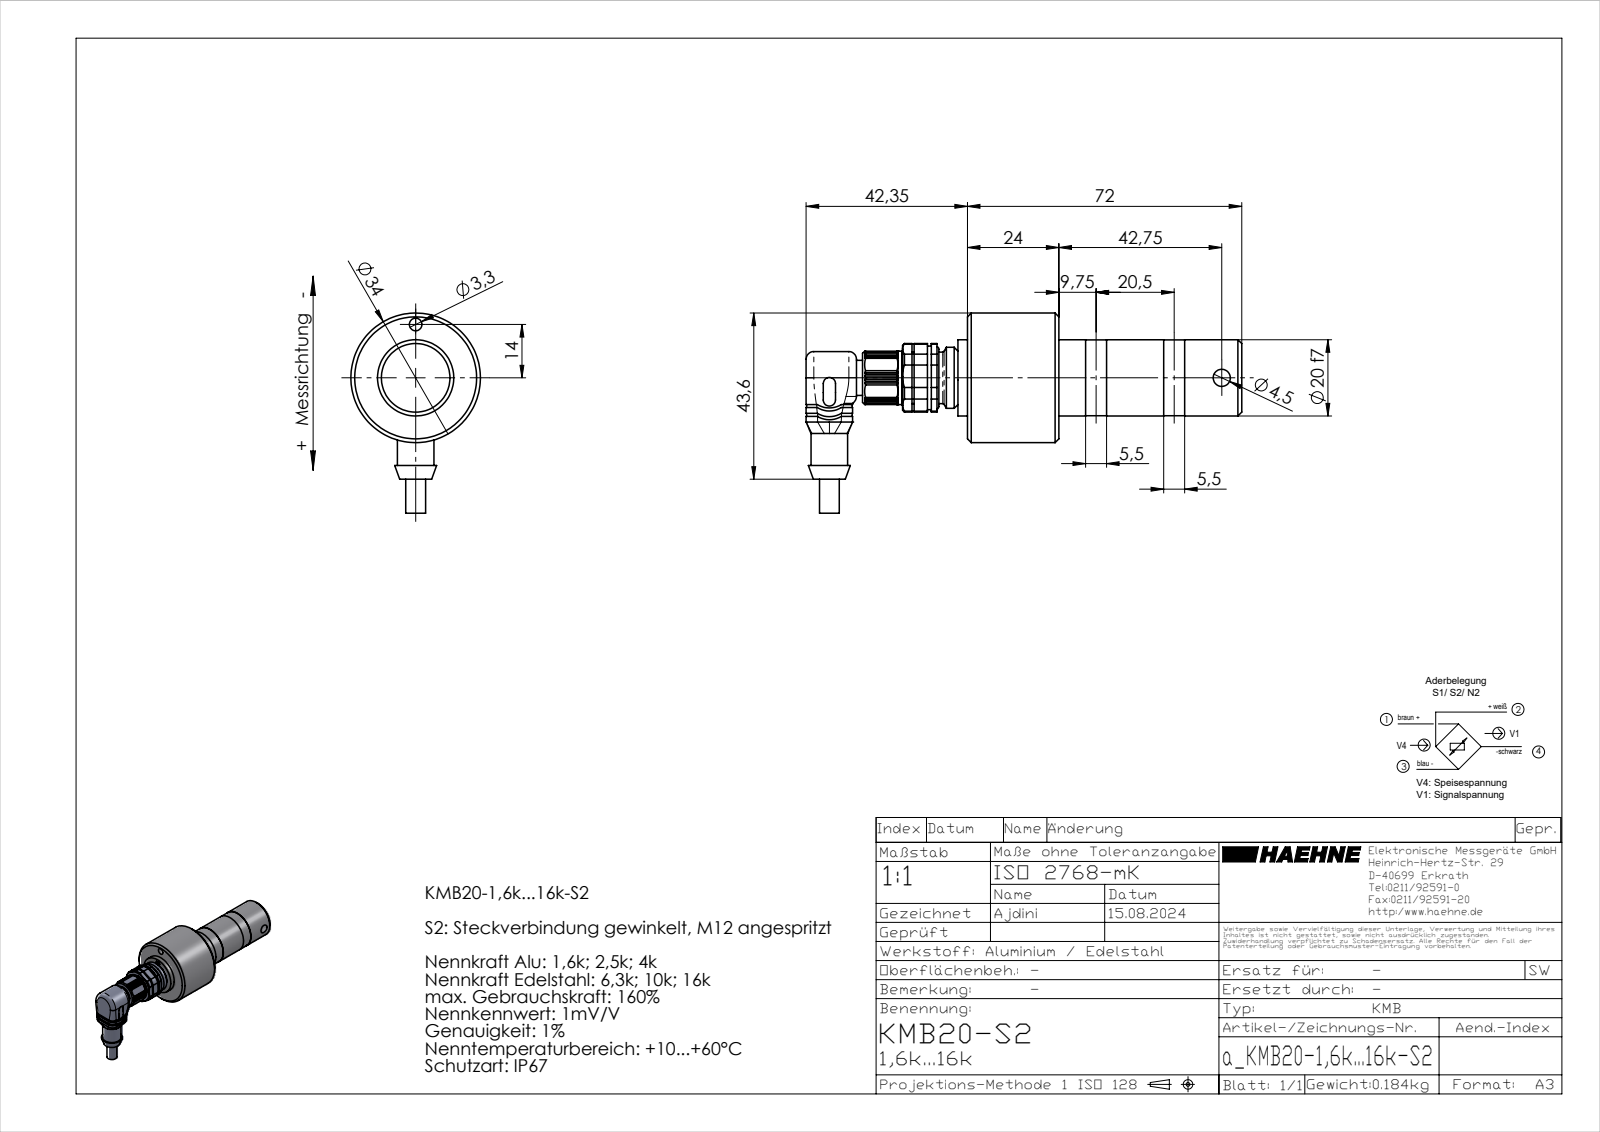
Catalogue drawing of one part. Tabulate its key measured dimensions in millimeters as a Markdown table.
| quantity | value |
| --- | --- |
| part name | a_KMB20-1,6k...16k-S2 |
| STEP written by | SolidWorks 2023 (AUTOMOTIVE_DESIGN) |
| units | millimeters |
| bodies | 4 solids, 719 faces (386 planar, 189 cylindrical, 144 other) |
| overall size | 114.35 × 52.52 × 34 |
| volume | 46 633 mm³ |
| surface area | 15 050 mm² |
| round holes (diameter × count) | 0.67 × 5, 1.1 × 4, 1.15 × 4, 1.6 × 4, 1.85 × 4, 1.2 × 1, 3.3 × 1, 4.5 × 1, 8.37 × 1, 8.42 × 1, 9.3 × 1, 10.16 × 1 |
| round bosses / shafts (diameter × count) | 1.8 × 4, 1.55 × 4, 1.5 × 4, 1 × 4, 34 × 1, 20 × 1, 19.9 × 1, 16.7 × 1 |
| partial cylindrical surfaces (radius × count) | 0.2 × 16, 0.3 × 9, 0.4 × 4, 0.53 × 4, 1 × 4, 1.27 × 4, 6 × 4, 1.6 × 2 |
| main face-to-face distances | 24, 2.5, 26.5, 48, 72, 74.5, 14, 14.55, 17.05, 89.05 |
| hole center spacings | 2.5, 3.54, 0.71, 1.14, 0.7, 1.15, 5, 7.02 |
